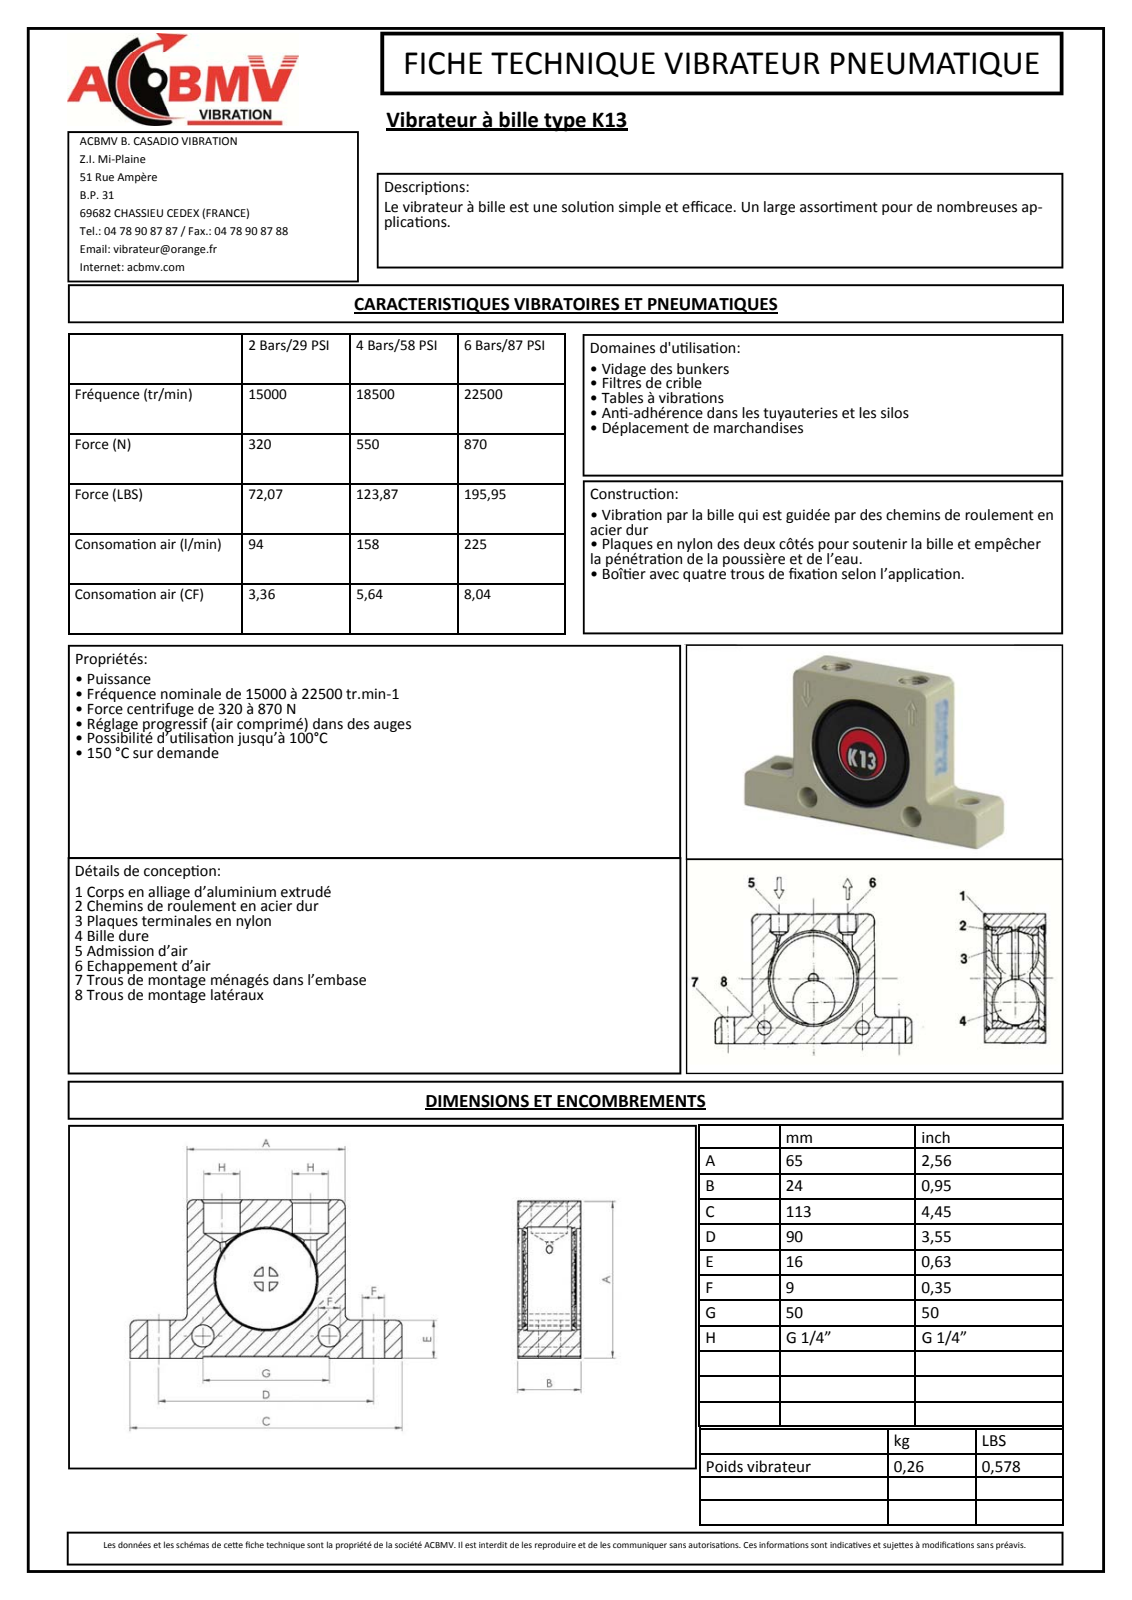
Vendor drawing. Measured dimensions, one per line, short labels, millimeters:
name: 1013-00-M
written by: Autodesk Inventor 2011 (CONFIG_CONTROL_DESIGN)
unit: mm
bodies: 1 solid, 380 faces (228 planar, 112 cylindrical, 40 other)
size: 113 × 65 × 24
volume: 73 973 mm³; area: 29 471 mm²
holes: 4× ⌀9, 2× ⌀11.45, 1× ⌀2, 1× ⌀2.09, 1× ⌀5, 1× ⌀15, 1× ⌀22, 1× ⌀24.5, 1× ⌀46.9, 1× ⌀47.9
bosses: 1× ⌀41, 1× ⌀23.5, 1× ⌀20.8, 1× ⌀1.88
rounds: 14× R0.3, 8× R11.25, 6× R3, 4× R0.25, 4× R0.54, 4× R0.9, 4× R1, 4× R1.7
face distances: 21, 24, 3, 65, 2, 1, 23, 20, 18, 0.5
hole spacings: 26.5, 32.65, 34.31, 63.5, 2.5, 37, 50, 90
